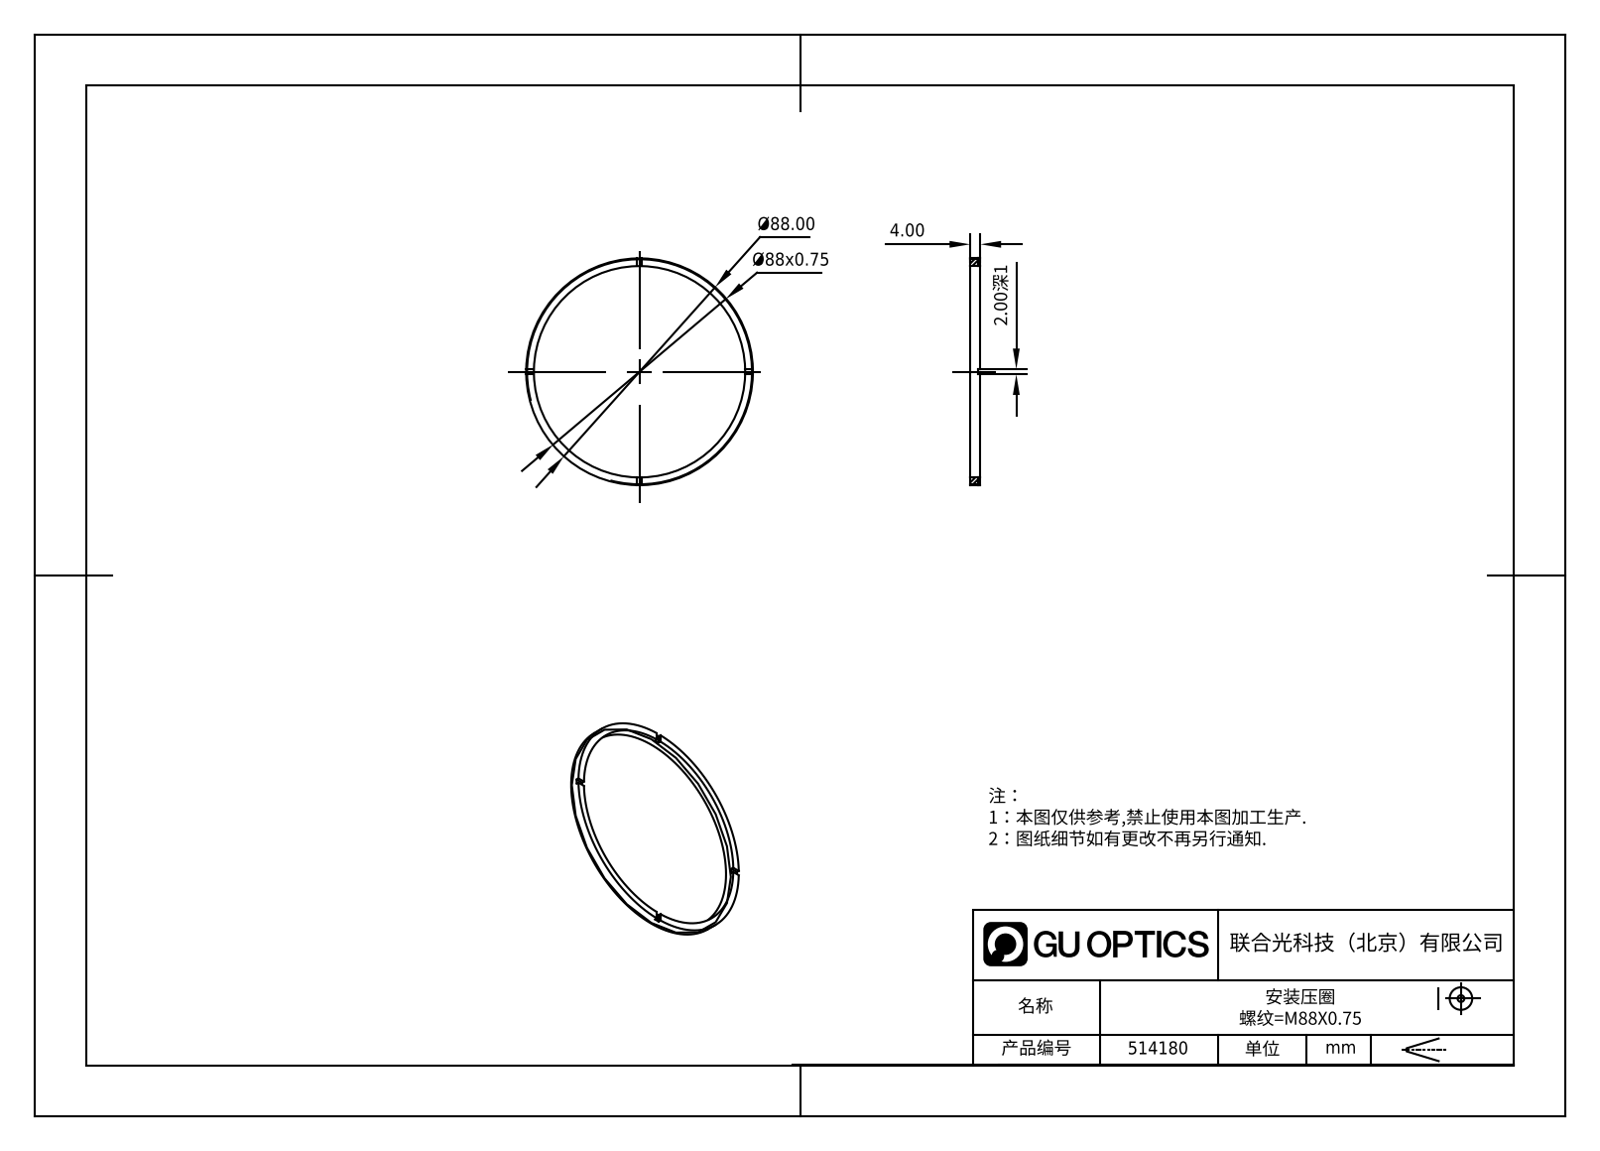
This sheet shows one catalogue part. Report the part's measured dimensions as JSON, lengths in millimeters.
{"part_name": "514180", "step_written_by": "SolidWorks 2020 (CONFIG_CONTROL_DESIGN)", "units": "millimeters", "bodies": {"solids": 1, "faces": 21, "planar": 17, "cylindrical": 4, "other": 0}, "overall_size": [88, 88, 4], "volume_mm3": 3180, "surface_area_mm2": 3746, "round_holes": [[82, 1]], "round_bosses_or_shafts": [[88, 1]], "face_to_face_distances": [4, 3, 1, 2]}
